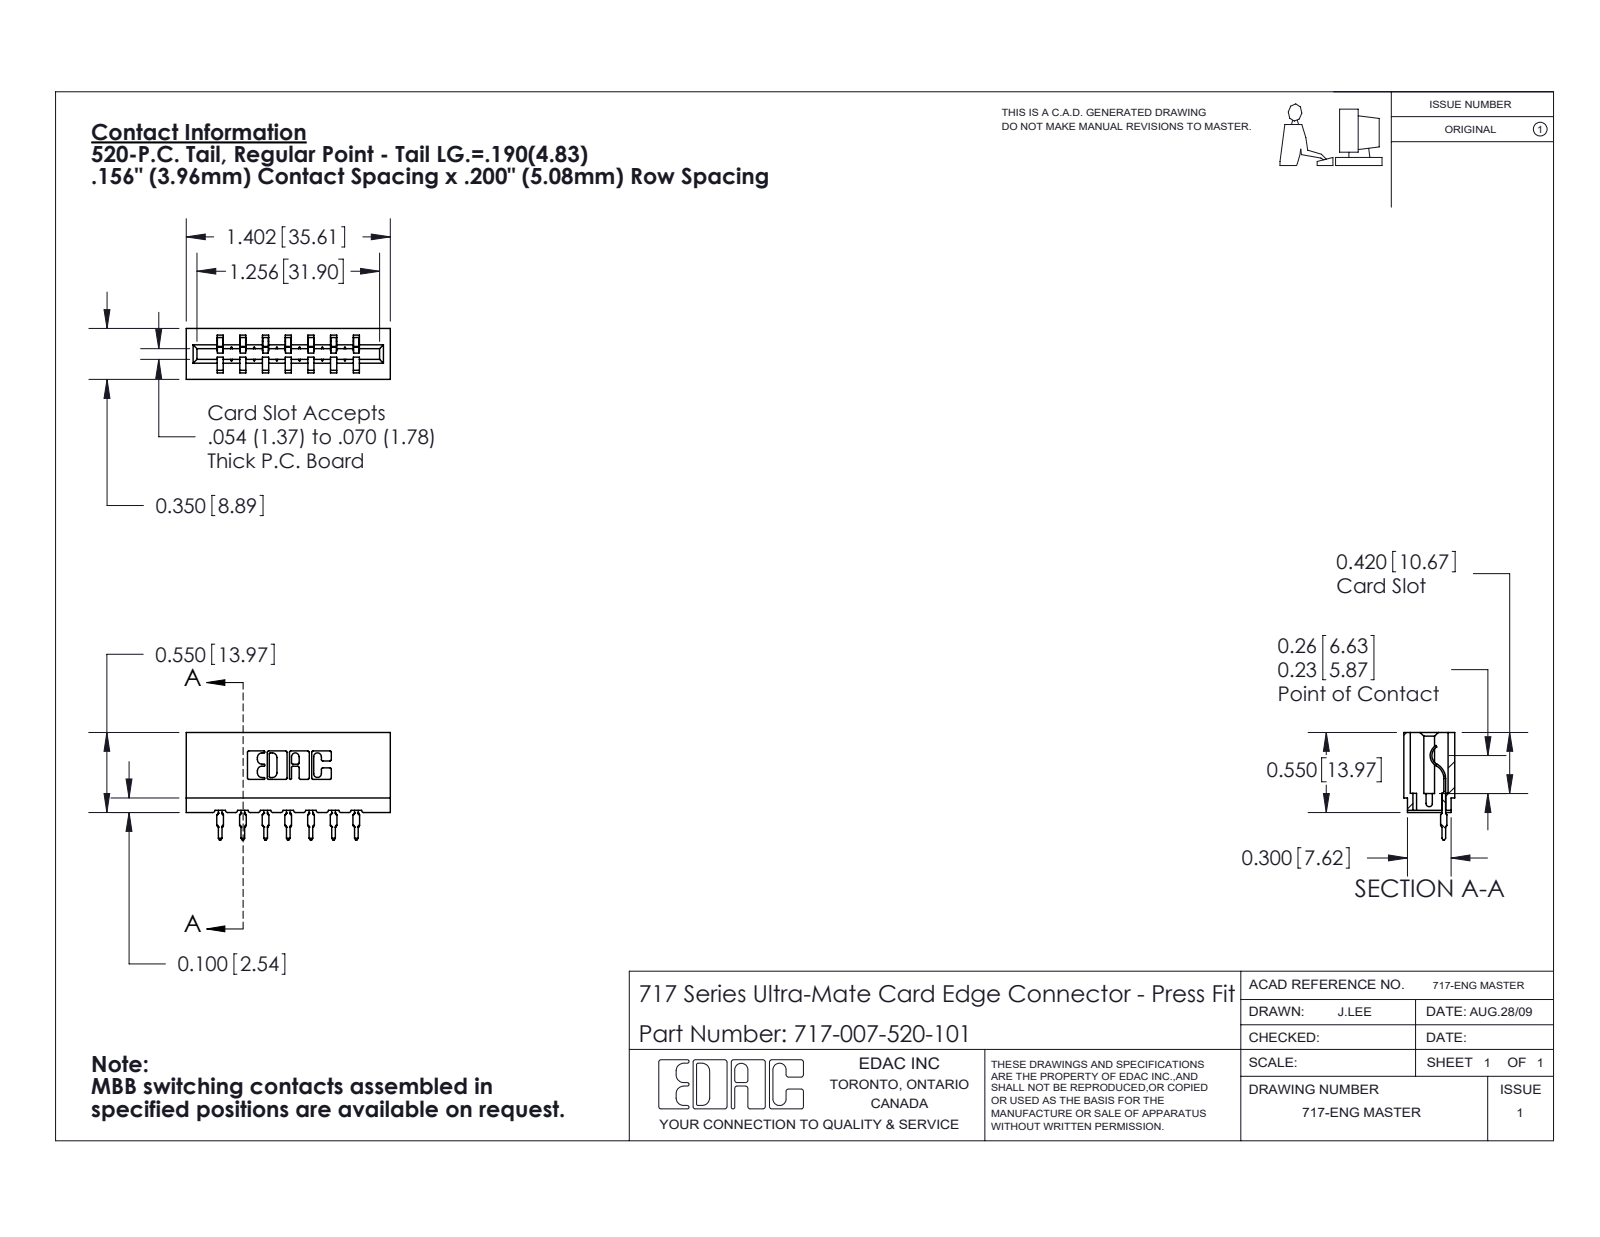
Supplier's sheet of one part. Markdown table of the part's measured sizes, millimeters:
| quantity | value |
| --- | --- |
| part name | 717 Part_Insulator Option - 06; 717-007-520-101; 745-292-001_520 |
| STEP written by | SolidWorks 2020 (CONFIG_CONTROL_DESIGN) |
| units | millimeters |
| bodies | 8 solids, 885 faces (530 planar, 173 cylindrical, 182 other) |
| overall size | 35.6 × 18.8 × 8.9 |
| volume | 3 160 mm³ |
| surface area | 4 003 mm² |
| partial cylindrical surfaces (radius × count) | 0.3 × 22, 0.4 × 14, 0.5 × 14, 0.2 × 6, 0.8 × 6, 0.1 × 4, 0.3 × 4, 0.7 × 3 |
| main face-to-face distances | 5.4, 4, 3.5, 8.9, 5, 7.9, 11.9, 15.8, 1.1, 6.9 |
